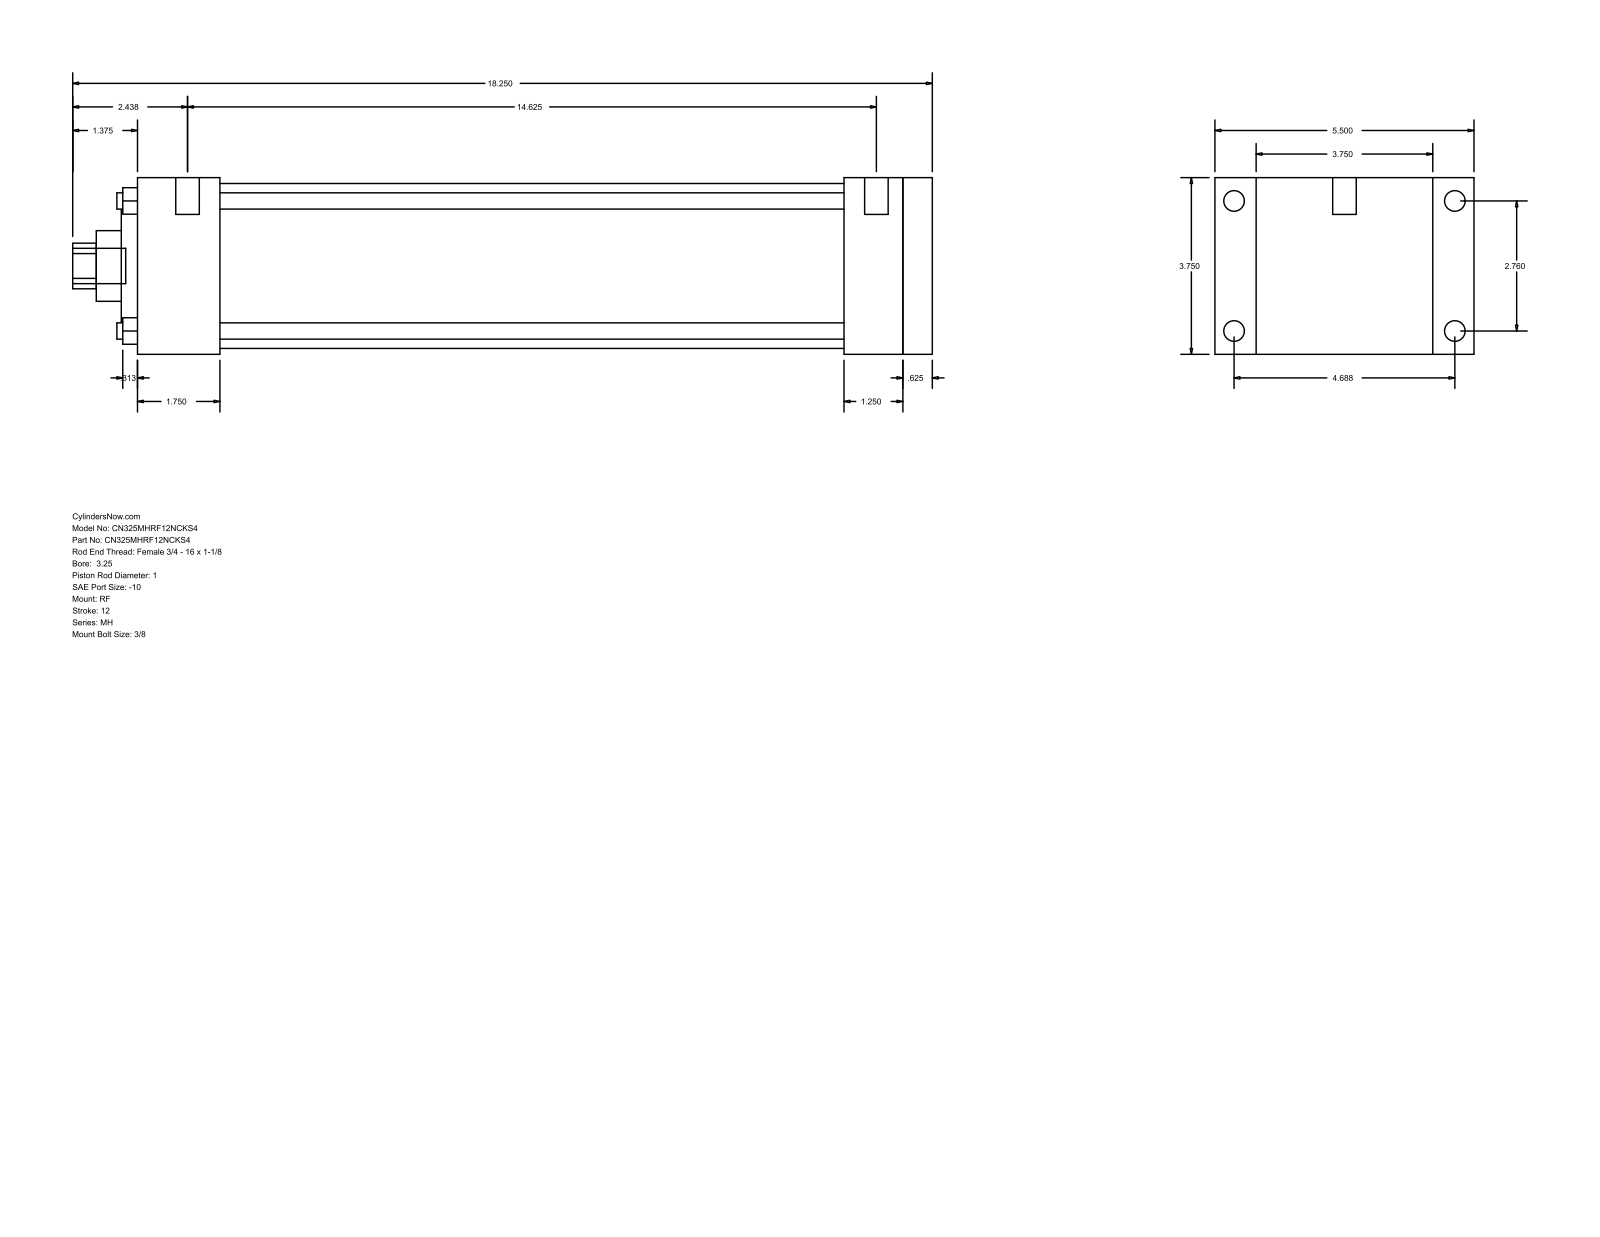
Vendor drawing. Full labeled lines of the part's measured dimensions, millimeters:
Part name (STEP PRODUCT): MH_RF__0325_1
STEP written by: GSSL Pune (CONFIG_CONTROL_DESIGN)
Units: millimetres
Bodies: 0 solids, 94 faces (65 planar, 29 cylindrical, 0 other)
Overall size (bounding box): 463.55 × 139.7 × 95.25
Round holes (diameter × count): ⌀8.76 ×4, ⌀25.4 ×1, ⌀38.1 ×1, ⌀60.33 ×1, ⌀88.9 ×1
Round bosses / shafts (diameter × count): ⌀11.13 ×4, ⌀5.56 ×4, ⌀12.7 ×2, ⌀19.05 ×1
Partial cylindrical surfaces — rounded edges, fillets, slot ends (radius × count): R12.29 ×1
Main face-to-face distances: 95.24, 428.63, 15.87, 412.76, 22.23, 117.47, 44.46, 368.3, 384.17, 381.01
Hole centre spacings: 49.57, 70.1, 99.14
